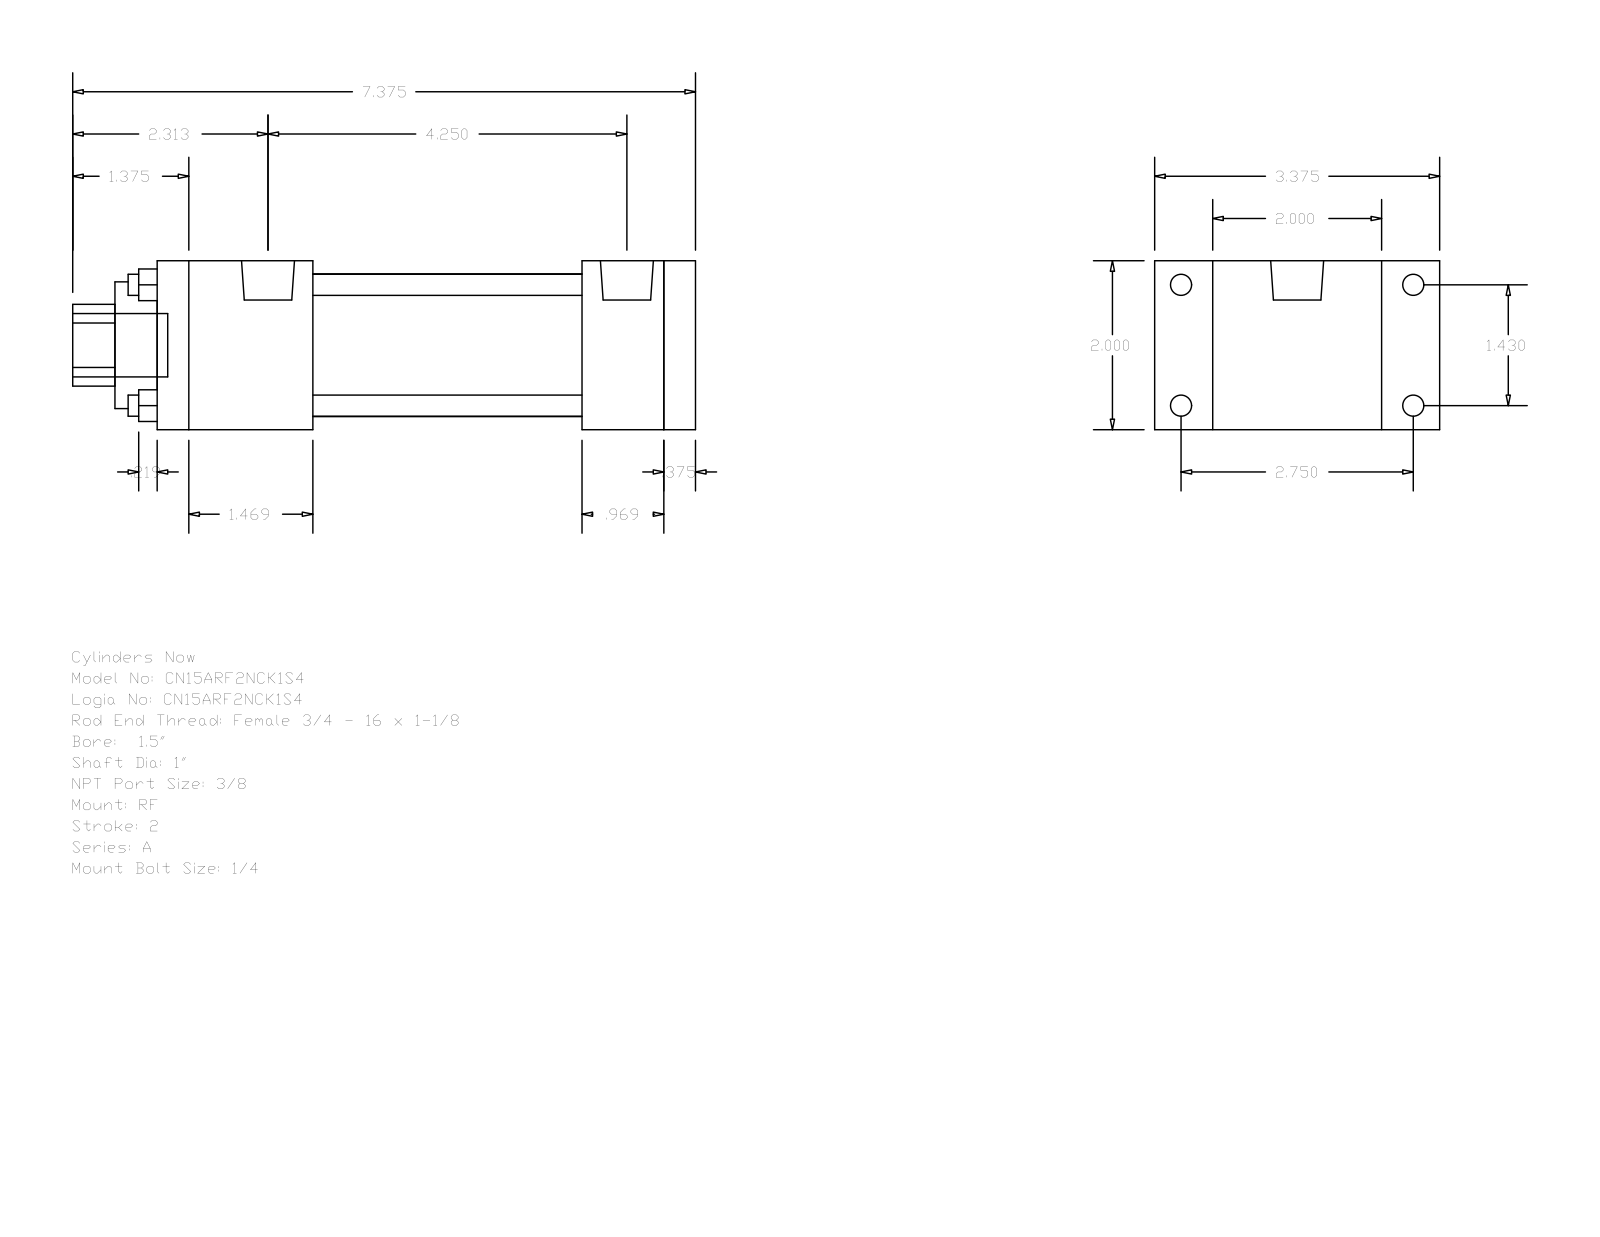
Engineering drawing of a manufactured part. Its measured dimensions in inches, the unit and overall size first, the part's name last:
Units: inches
Overall size (bounding box): 7.375 × 3.375 × 2
Round holes (diameter × count): ⌀0.25 ×4, ⌀1 ×1, ⌀1.5 ×1, ⌀1.69 ×1
Round bosses / shafts (diameter × count): ⌀0.25 ×4, ⌀0.219 ×4, ⌀0.627 ×2, ⌀0.75 ×1
Partial cylindrical surfaces — rounded edges, fillets, slot ends (radius × count): R0.484 ×1
Main face-to-face distances: 2, 0.375, 6, 6.375, 5.031, 0.969, 1.344, 1.844, 3.187, 4.156
Hole centre spacings: 1.011, 1.43, 2.022
Bodies: 0 solids, 92 faces (64 planar, 28 cylindrical, 0 other)
Part name (STEP PRODUCT): A_RF__0150_1
STEP written by: GSSL Pune (CONFIG_CONTROL_DESIGN)
